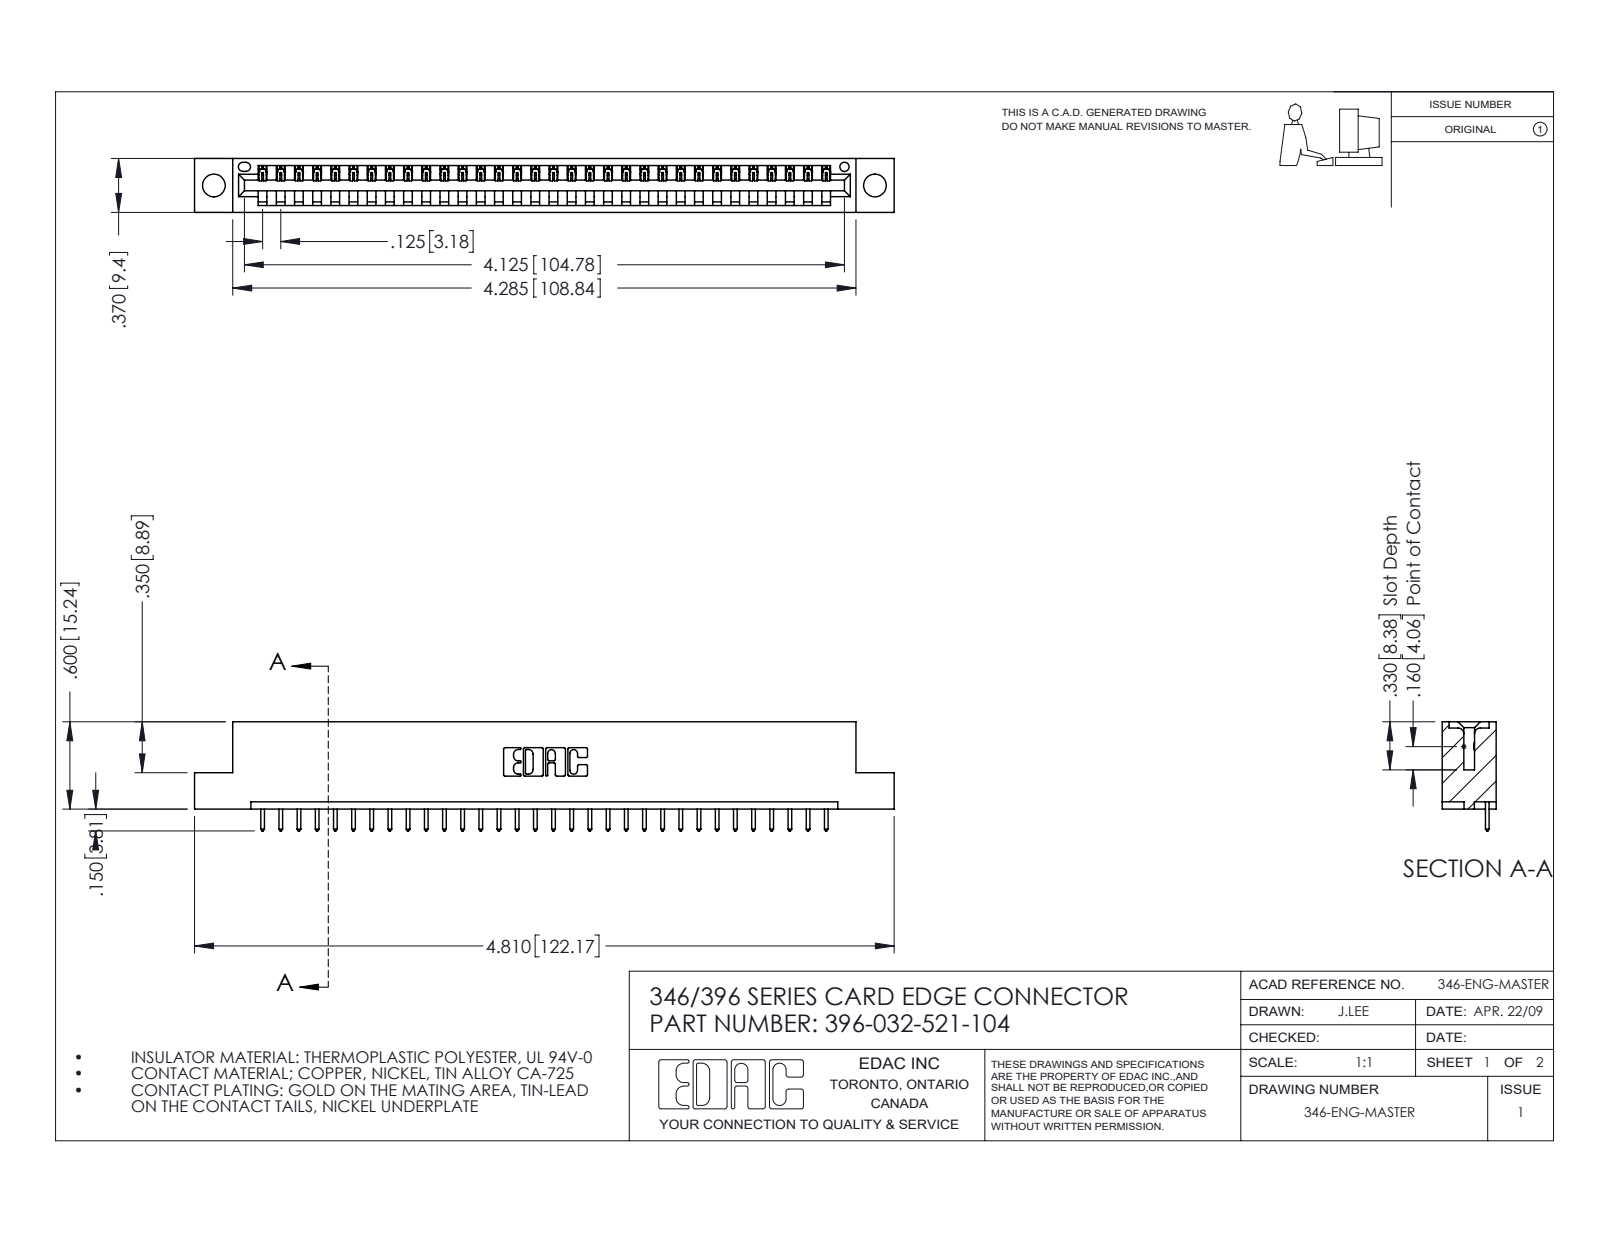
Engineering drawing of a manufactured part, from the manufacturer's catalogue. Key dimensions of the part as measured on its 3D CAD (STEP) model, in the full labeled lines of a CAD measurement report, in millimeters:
Part name (STEP PRODUCT): 346 Part_Flush Mounting Lugs - 0.156 Dia-TH; 396-032-521-104; 345-292-001_345-293-121
STEP written by: SolidWorks 2016 (CONFIG_CONTROL_DESIGN)
Units: millimetres
Bodies: 33 solids, 1978 faces (1356 planar, 622 cylindrical, 0 other)
Overall size (bounding box): 122.2 × 19.1 × 9.4
Volume: 11 500 mm³ · Surface area: 13 650 mm²
Round holes (diameter × count): ⌀4 ×2, ⌀1.6 ×1
Partial cylindrical surfaces — rounded edges, fillets, slot ends (radius × count): R0.2 ×64, R0.3 ×64, R0.3 ×22, R0.2 ×6, R0.8 ×6, R0.7 ×3, R0.8 ×2, R1 ×2
Main face-to-face distances: 1.2, 8.2, 9.4, 6.4, 1.8, 7.6, 0.6, 3.8, 5.6, 2.5
Hole centre spacings: 6.2, 110.2, 115.4
